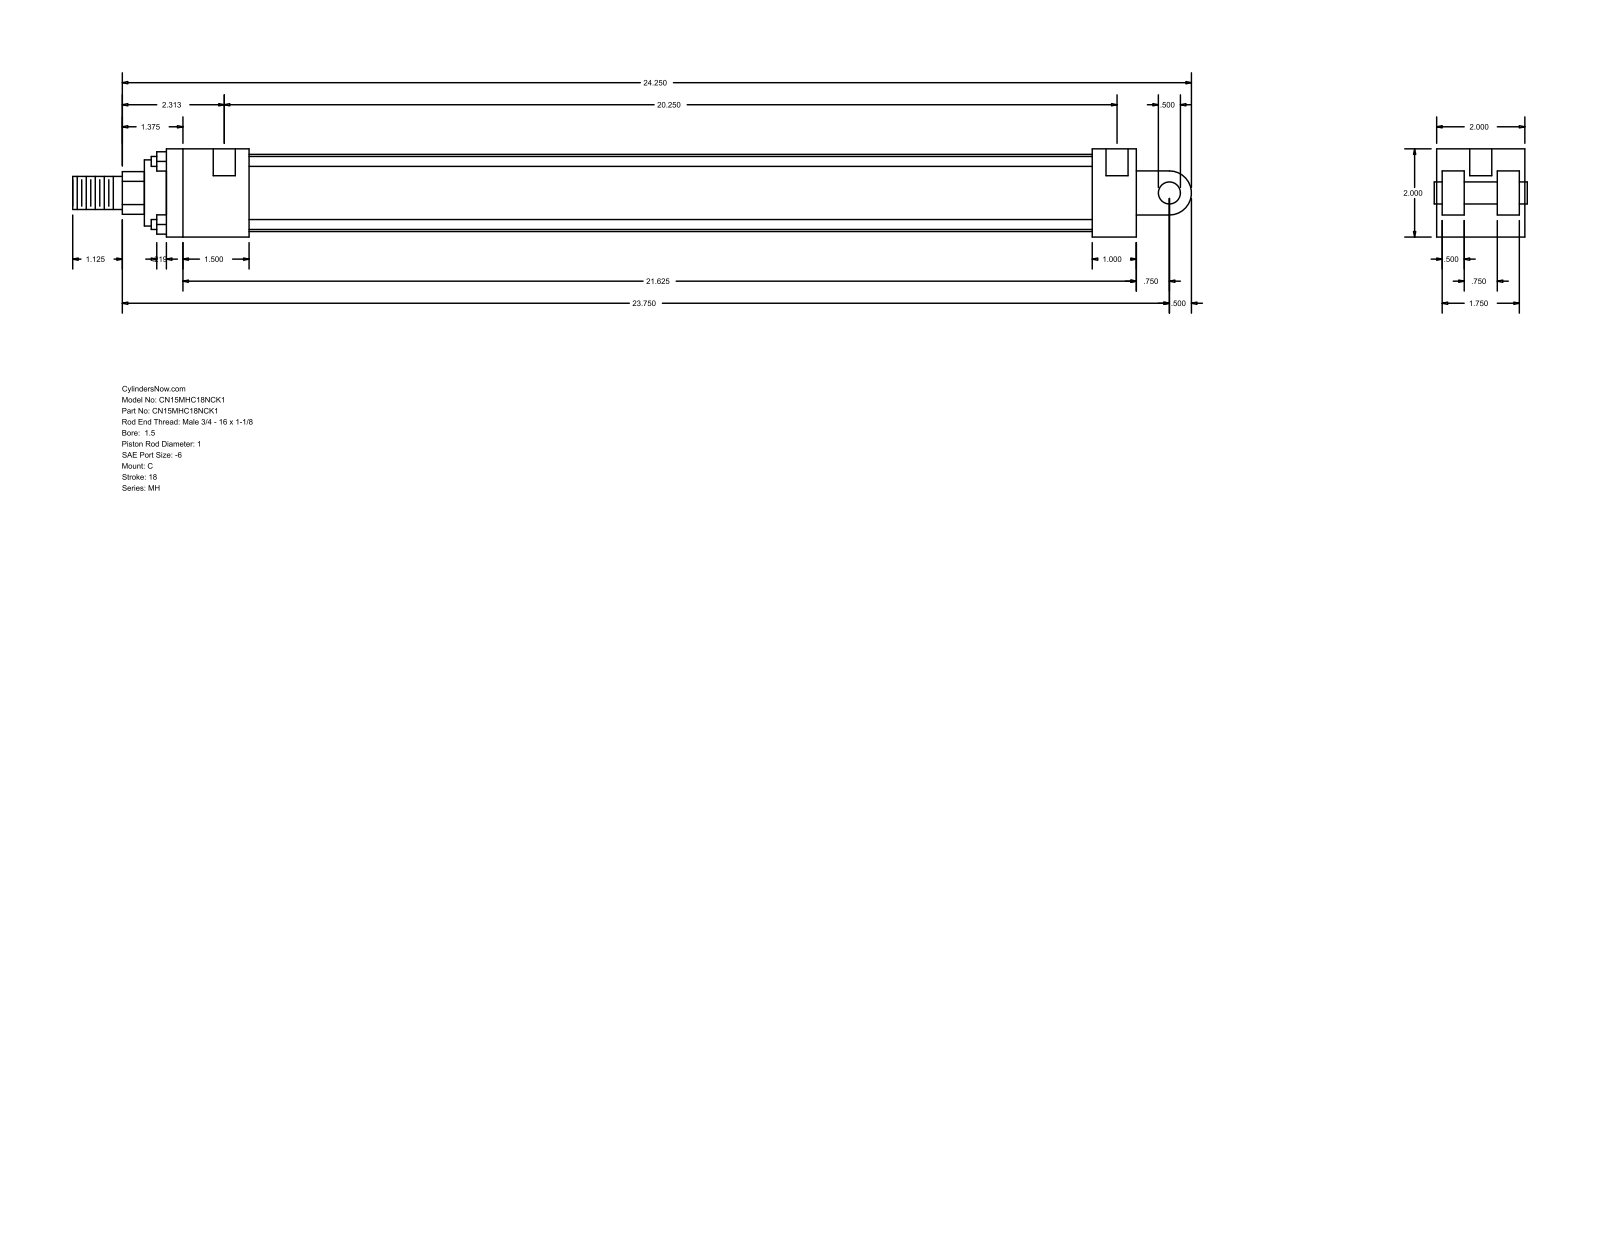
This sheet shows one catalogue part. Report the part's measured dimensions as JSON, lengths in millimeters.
{"part_name": "MH_C__0150_1", "step_written_by": "GSSL Pune (CONFIG_CONTROL_DESIGN)", "units": "millimeters", "bodies": {"solids": 0, "faces": 99, "planar": 70, "cylindrical": 29, "other": 0}, "overall_size": [644.52, 50.8, 50.8], "round_holes": [[5.56, 4], [12.7, 2]], "round_bosses_or_shafts": [[5.71, 4], [44.45, 1], [38.1, 1], [25.4, 1], [19.05, 1], [12.7, 1]], "partial_cylinders_radius": [[12.29, 1], [12.7, 1]], "face_to_face_distances": [50.8, 12.7, 47.63, 25.4, 3.17, 15.87, 34.93, 31.76, 558.8, 38.1], "hole_center_spacings": [517.53, 3.18, 514.35]}
